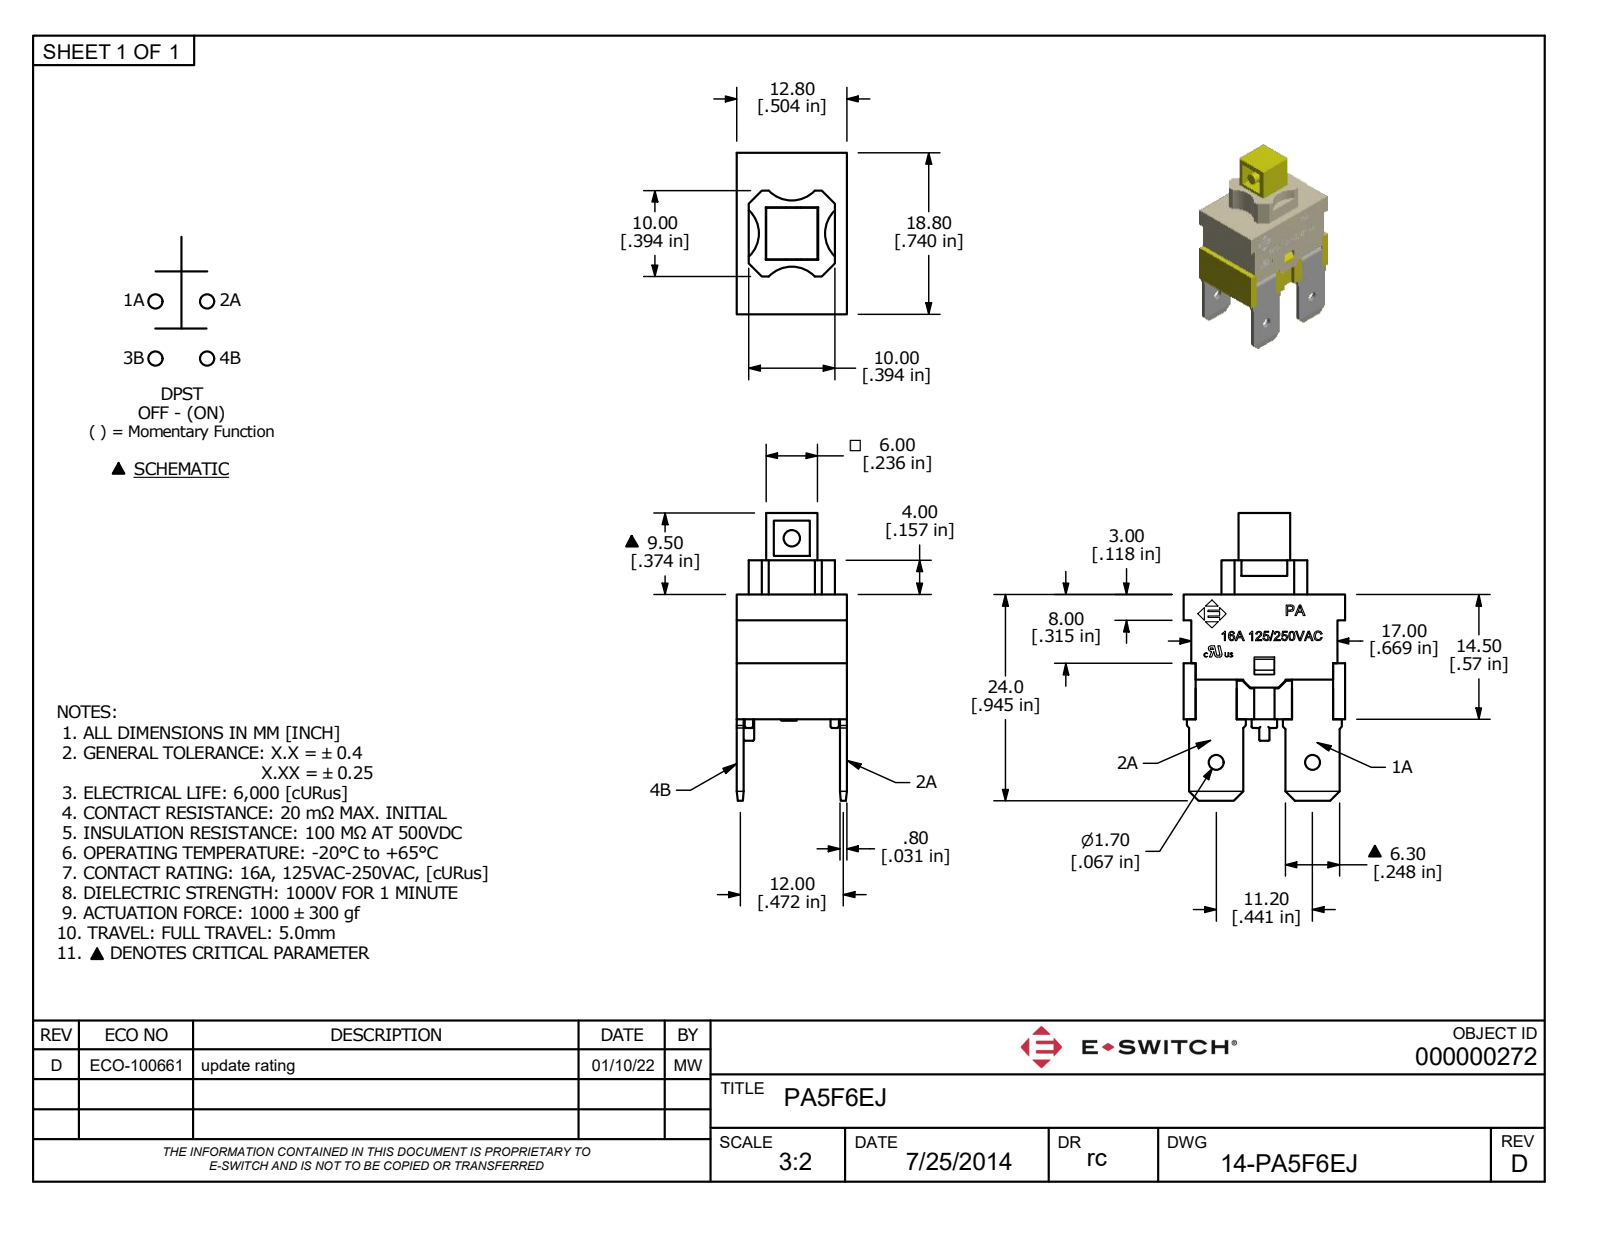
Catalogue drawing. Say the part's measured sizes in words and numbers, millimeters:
The part is named "PA5F6EJ". Its 3-D file was written by "Autodesk Inventor 2022 (AUTOMOTIVE_DESIGN)". It is 1 solid with 849 faces: 632 planar, 86 cylindrical and 131 other. Overall it measures 33.5 by 18.8 by 12.8 millimeters. Its volume is 2 286 cubic millimeters and its surface area 4 701 square millimeters. Round holes: 2 of diameter 1.7, 1 of diameter 3. Round bosses or shafts: 4 of diameter 0.95, 2 of diameter 2.5, 1 of diameter 1.9. Partial cylindrical surfaces (rounded edges, fillets, slot ends): 26 of radius 0.25, 16 of radius 0.12, 8 of radius 0.15, 4 of radius 1, 4 of radius 3.71, 1 of radius 0.5, 1 of radius 1.79, 1 of radius 2.32. The main face-to-face distances are 0.8, 12, 12.8, 0.9, 16.8, 2, 11.2, 5.5, 8.6, 1.1. The hole center spacings are 11.2.
